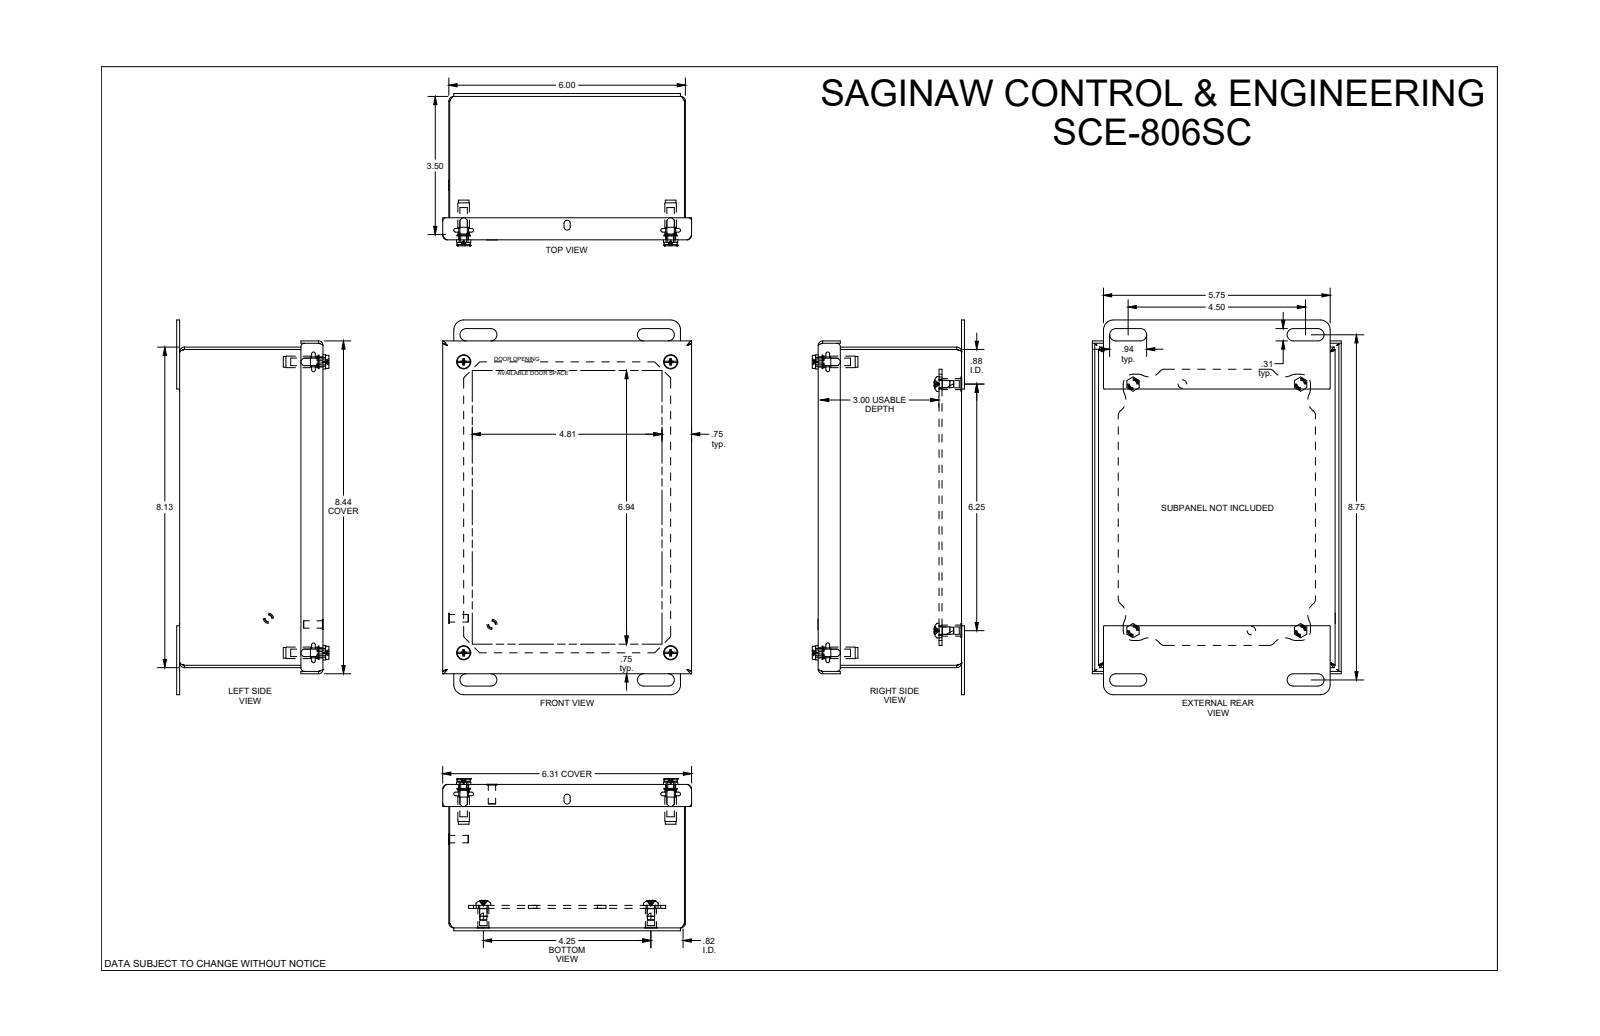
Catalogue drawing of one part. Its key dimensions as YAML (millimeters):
part_name: "SCE-806SC"
step_written_by: "SolidWorks 2019 (CONFIG_CONTROL_DESIGN)"
units: millimeters
bodies: {solids: 0, faces: 879, planar: 397, cylindrical: 216, other: 266}
overall_size: [241.3, 160.4, 98.1]
round_holes:
  - {diameter: 4.8, count: 8}
  - {diameter: 6.4, count: 8}
  - {diameter: 5.6, count: 4}
  - {diameter: 6.8, count: 4}
  - {diameter: 7.1, count: 4}
  - {diameter: 8.1, count: 4}
  - {diameter: 4.9, count: 2}
  - {diameter: 5.5, count: 2}
round_bosses_or_shafts:
  - {diameter: 4.8, count: 10}
  - {diameter: 9.5, count: 4}
  - {diameter: 9.2, count: 4}
  - {diameter: 8.6, count: 4}
  - {diameter: 8.5, count: 4}
  - {diameter: 7.4, count: 4}
  - {diameter: 7.1, count: 4}
  - {diameter: 6.9, count: 4}
partial_cylinders:
  - {radius: 3.2, count: 16}
  - {radius: 6.4, count: 16}
  - {radius: 0.1, count: 8}
  - {radius: 0.2, count: 8}
  - {radius: 1.3, count: 8}
  - {radius: 2.8, count: 8}
  - {radius: 4, count: 8}
  - {radius: 6.5, count: 8}
face_to_face_distances: [1.5, 1.5, 90.8, 89.3, 150.9, 92.3, 90.8, 78.2, 14.5, 13]
hole_center_spacings: [19.1, 210.9, 173.5, 121.5, 133.4, 133.4, 187.3, 187.3]
